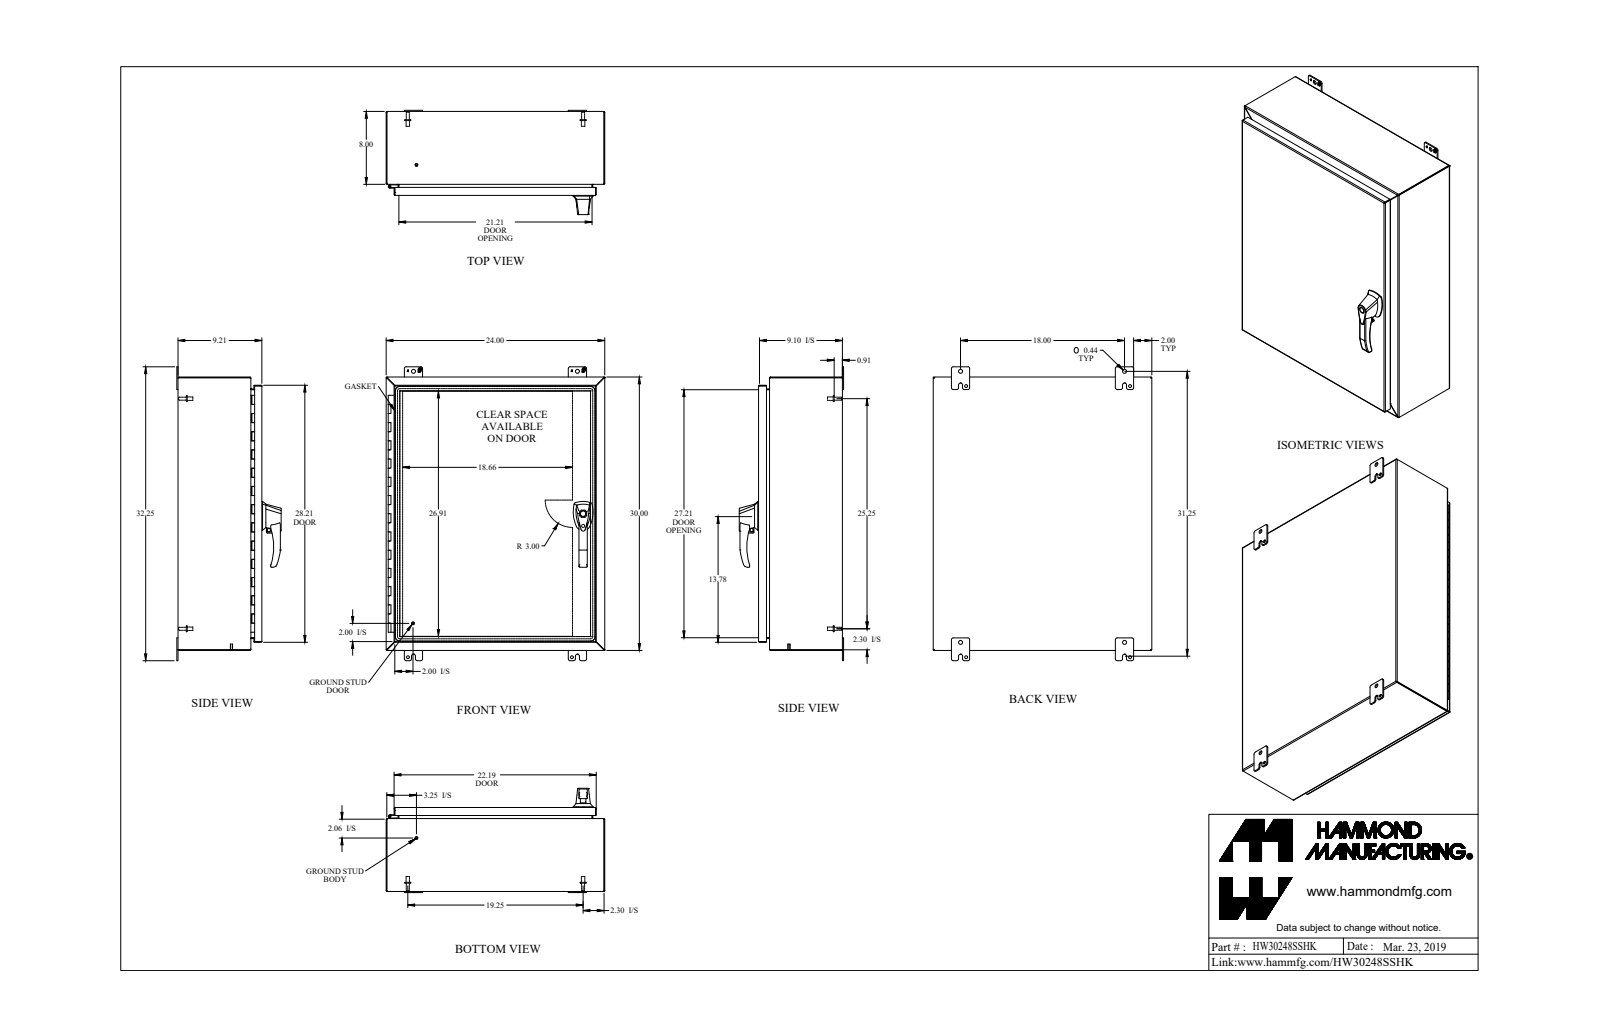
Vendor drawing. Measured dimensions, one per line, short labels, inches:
name: HW30248SSHK
written by: SolidWorks 2018 (AUTOMOTIVE_DESIGN)
unit: in
bodies: 42 solids, 1476 faces (723 planar, 599 cylindrical, 154 other)
size: 32.25 × 24 × 11.45
volume: 218.9 in³; area: 5 674 in²
holes: 6× ⌀0.176, 5× ⌀0.313, 3× ⌀0.25, 3× ⌀0.265, 3× ⌀0.413, 2× ⌀0.196, 2× ⌀0.256, 2× ⌀0.394, 2× ⌀0.437, 1× ⌀0.187, 1× ⌀0.233, 1× ⌀0.33
bosses: 9× ⌀0.375, 7× ⌀0.25, 6× ⌀0.156, 4× ⌀0.65, 4× ⌀0.332, 3× ⌀1, 3× ⌀0.51, 2× ⌀0.63
rounds: 27× R0.25, 24× R0.188, 20× R0.036, 20× R0.108, 12× R0.06, 9× R0.125, 8× R0.045, 8× R0.218
face distances: 0.072, 0.072, 9.138, 9.066, 9.138, 9.21, 23.928, 29.928, 7.928, 23.856
hole spacings: 1.11, 11.118, 11.119, 22.237, 11.119, 18, 23.752, 31.381
